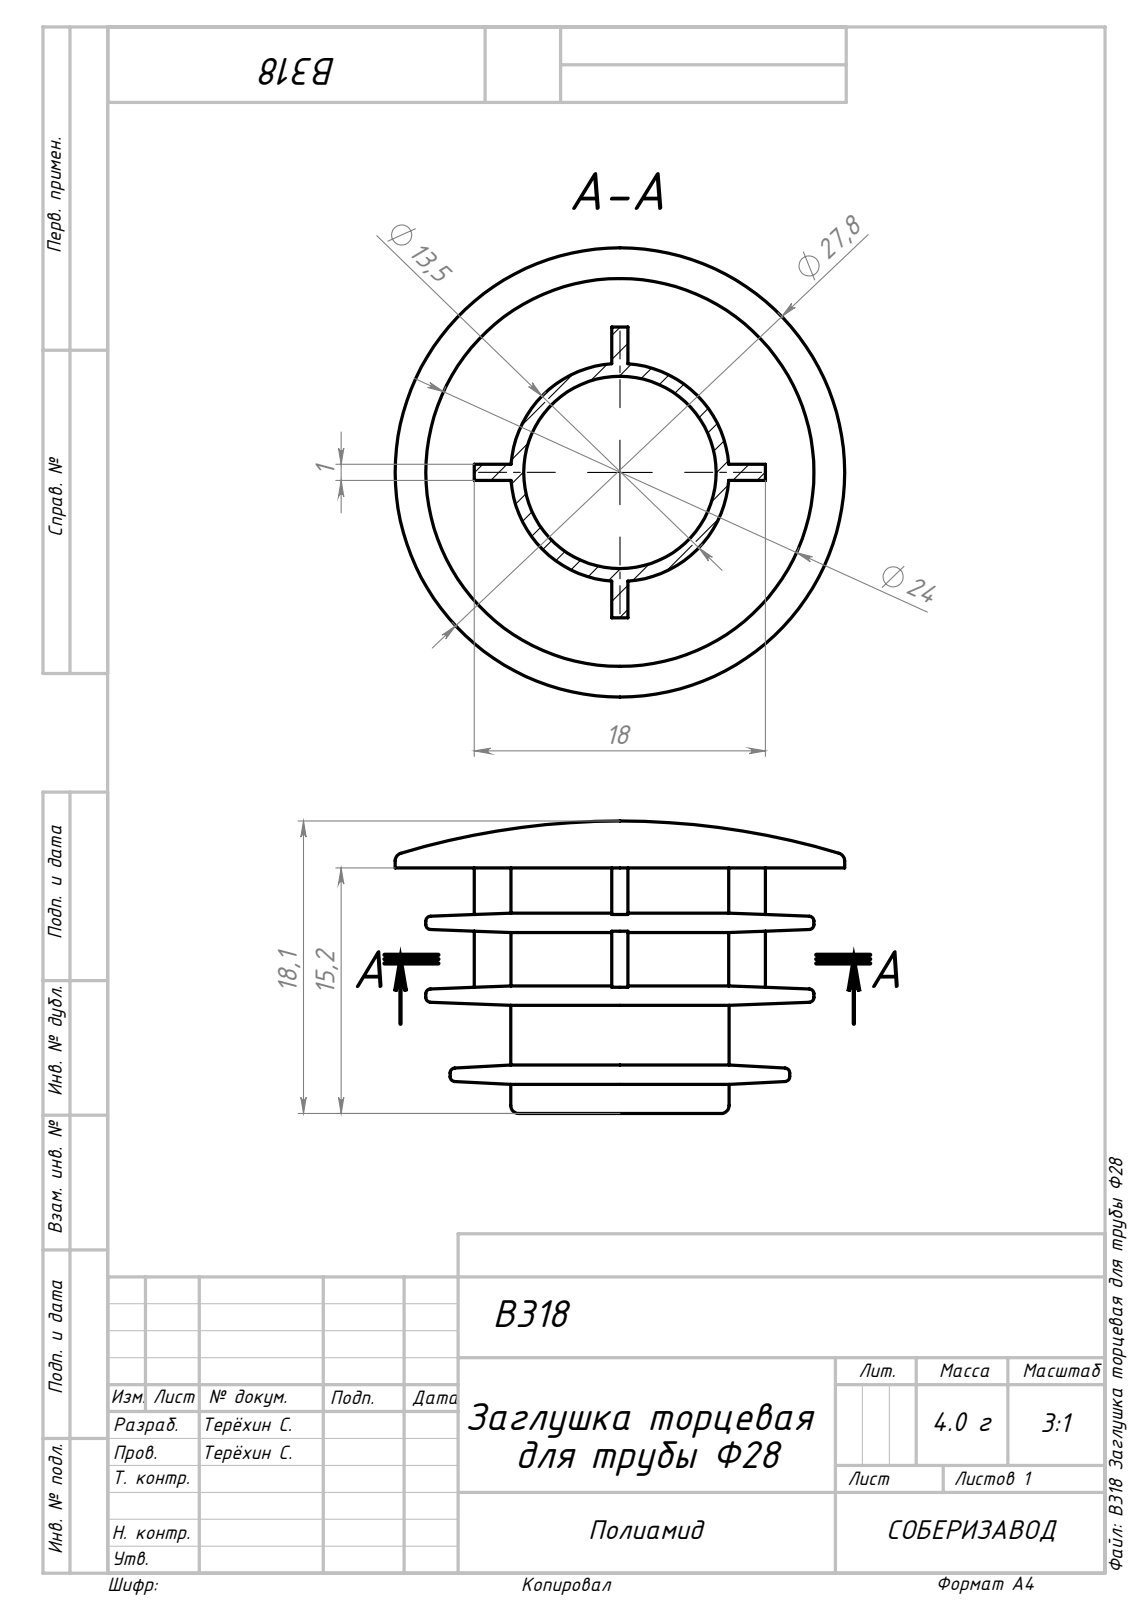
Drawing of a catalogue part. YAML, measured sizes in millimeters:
part_name: "B318 Заглушка торцевая для трубы Ф28"
step_written_by: "SolidWorks 2022 (AUTOMOTIVE_DESIGN)"
units: millimeters
bodies: {solids: 1, faces: 80, planar: 26, cylindrical: 22, other: 32}
overall_size: [27.8, 27.8, 18.1]
volume: 2442
surface_area: 4186
round_holes:
  - {diameter: 11.9, count: 1}
round_bosses_or_shafts:
  - {diameter: 27.8, count: 1}
  - {diameter: 24, count: 1}
  - {diameter: 21, count: 1}
  - {diameter: 13.5, count: 1}
face_to_face_distances: [1, 8.5, 9.5, 18, 15.2]
